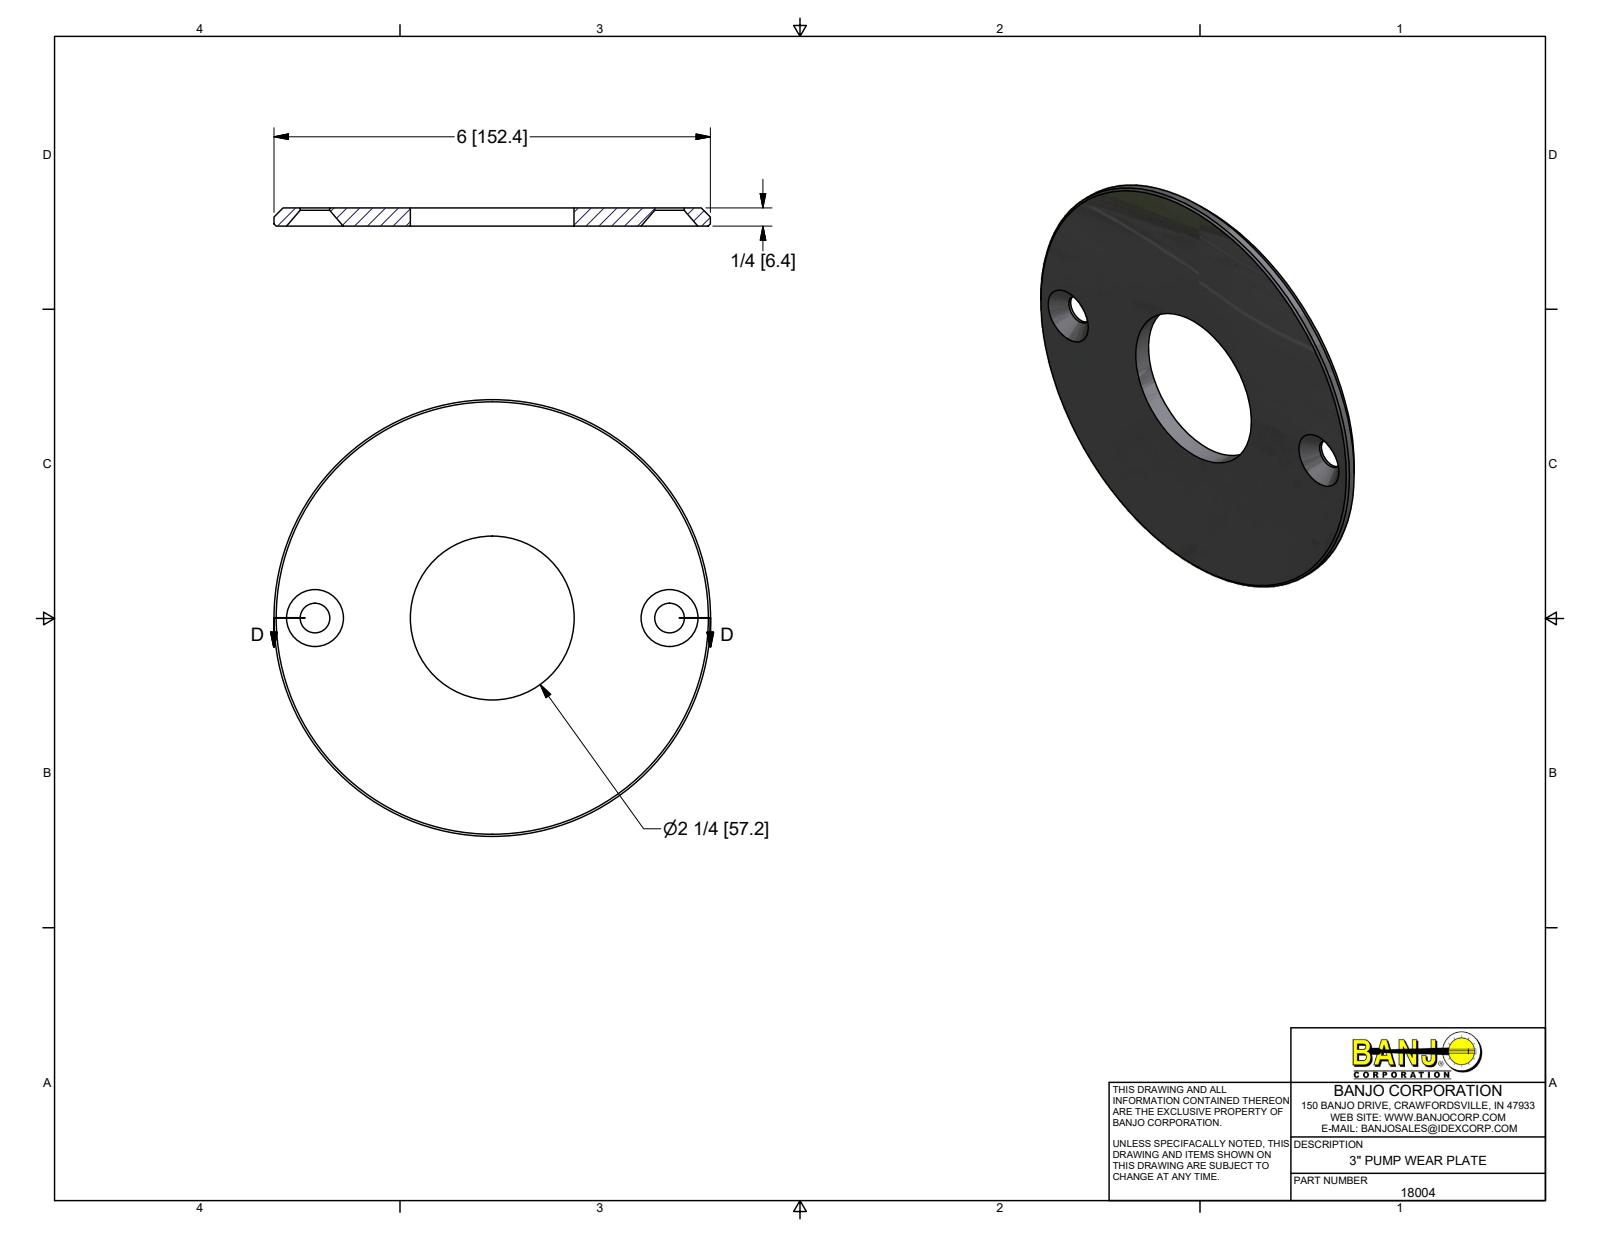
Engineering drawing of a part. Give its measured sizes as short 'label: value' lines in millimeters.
name: 18004
written by: Autodesk Inventor 2017 (AUTOMOTIVE_DESIGN)
unit: mm
bodies: 1 solid, 10 faces (2 planar, 4 cylindrical, 4 other)
size: 152.4 × 152.4 × 6.35
volume: 94 858 mm³; area: 34 373 mm²
holes: 2× ⌀10.32, 1× ⌀57.15
bosses: 1× ⌀152.4
face distances: 6.35
hole spacings: 61.91, 123.82
